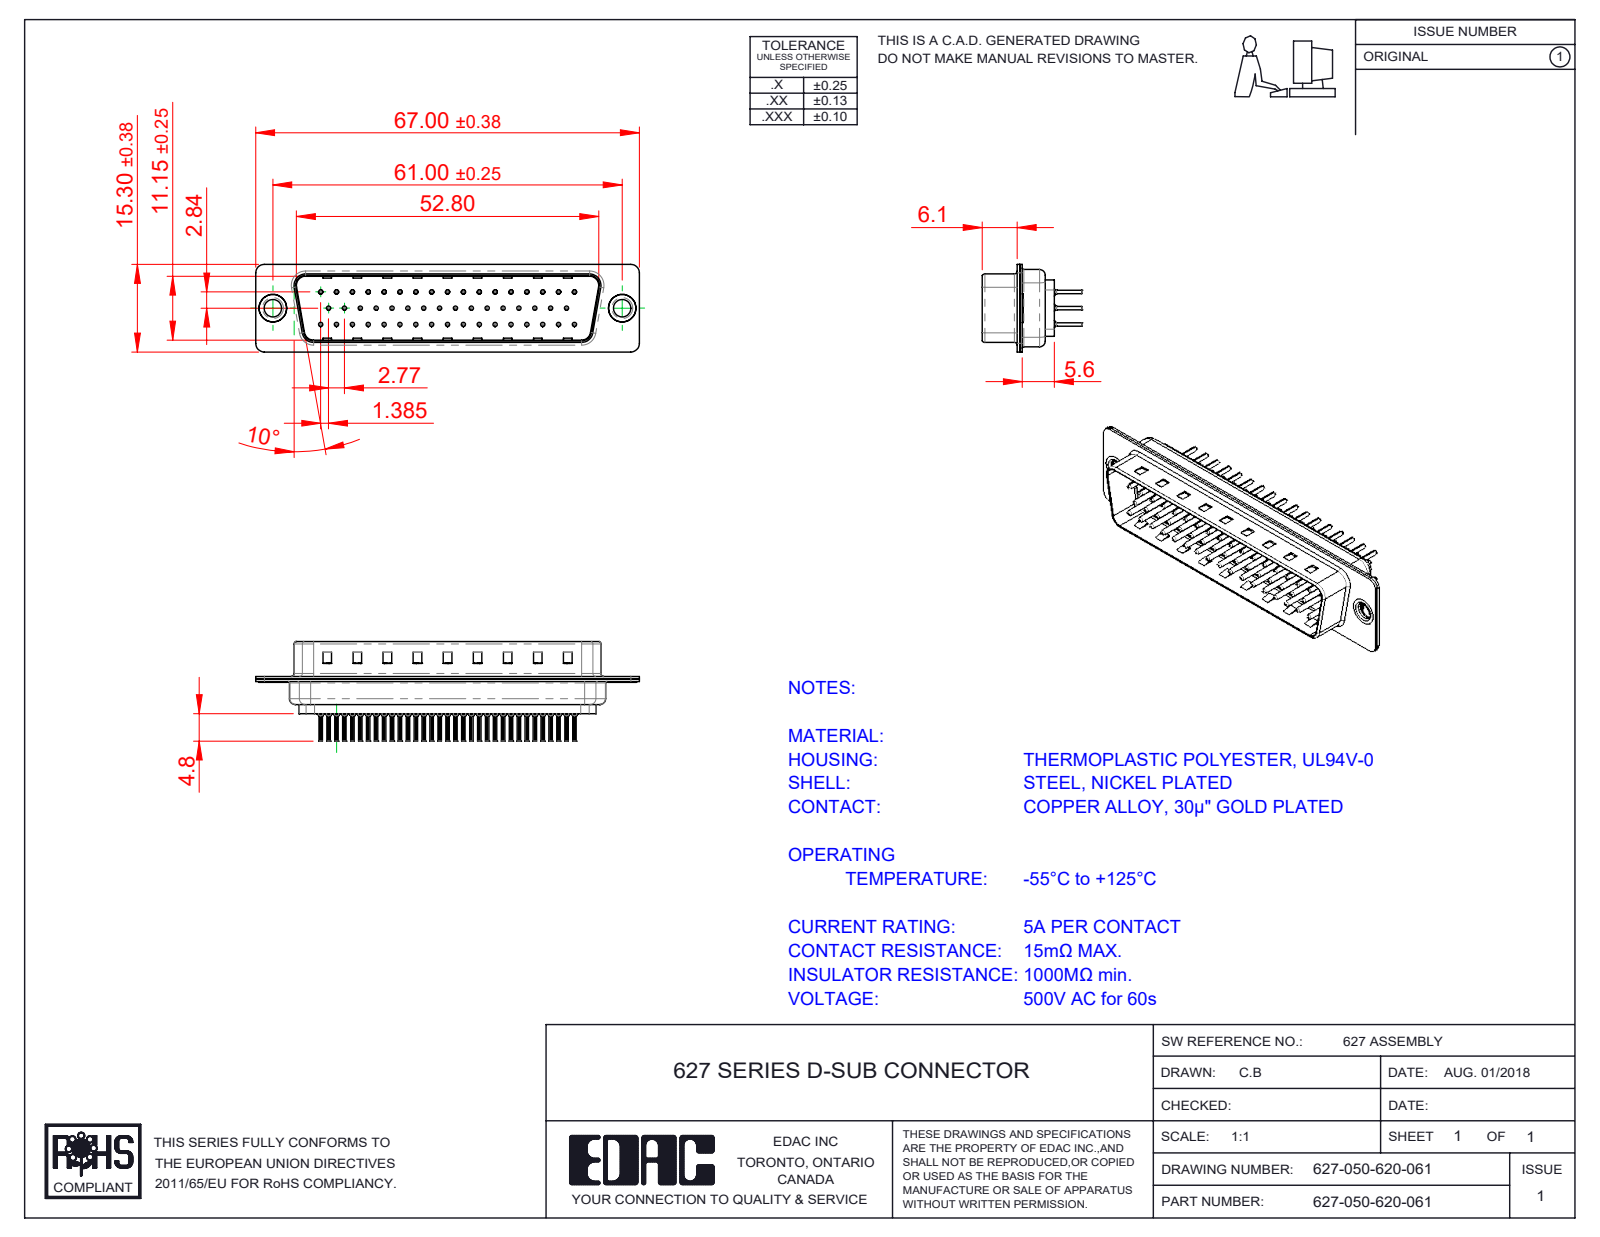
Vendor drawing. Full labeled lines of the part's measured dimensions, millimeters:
Part name (STEP PRODUCT): 627 Shell Rear_50 Contacts; 627 Contact Row 1_20L; 627 Thru Hole Rivet; 627 Shell Front_50 Contacts (+4 more)
STEP written by: SolidWorks 2020 (CONFIG_CONTROL_DESIGN)
Units: millimetres
Bodies: 55 solids, 5286 faces (1403 planar, 1975 cylindrical, 1908 other)
Overall size (bounding box): 67 × 17.3 × 15.3
Volume: 4 346 mm³ · Surface area: 12 440 mm²
Round holes (diameter × count): ⌀0.2 ×50, ⌀0.35 ×50, ⌀1.1 ×50, ⌀1.6 ×50, ⌀3.05 ×2, ⌀4 ×2, ⌀4.8 ×2
Round bosses / shafts (diameter × count): ⌀2 ×50, ⌀1.5 ×50, ⌀0.75 ×50, ⌀0.6 ×50, ⌀5 ×2, ⌀4.9 ×2, ⌀3.55 ×2
Partial cylindrical surfaces — rounded edges, fillets, slot ends (radius × count): R0.1 ×100, R1.5 ×16, R2 ×12, R0.5 ×8, R1.6 ×8, R0.25 ×4, R0.6 ×4, R0.65 ×4
Main face-to-face distances: 0.4, 0.45, 11.55, 0.9, 6.05, 6.5, 0.78, 12.33, 1.95, 0.77
Hole centre spacings: 3.16, 2.77, 5.54, 8.31, 11.08, 13.85, 16.62, 5.03
